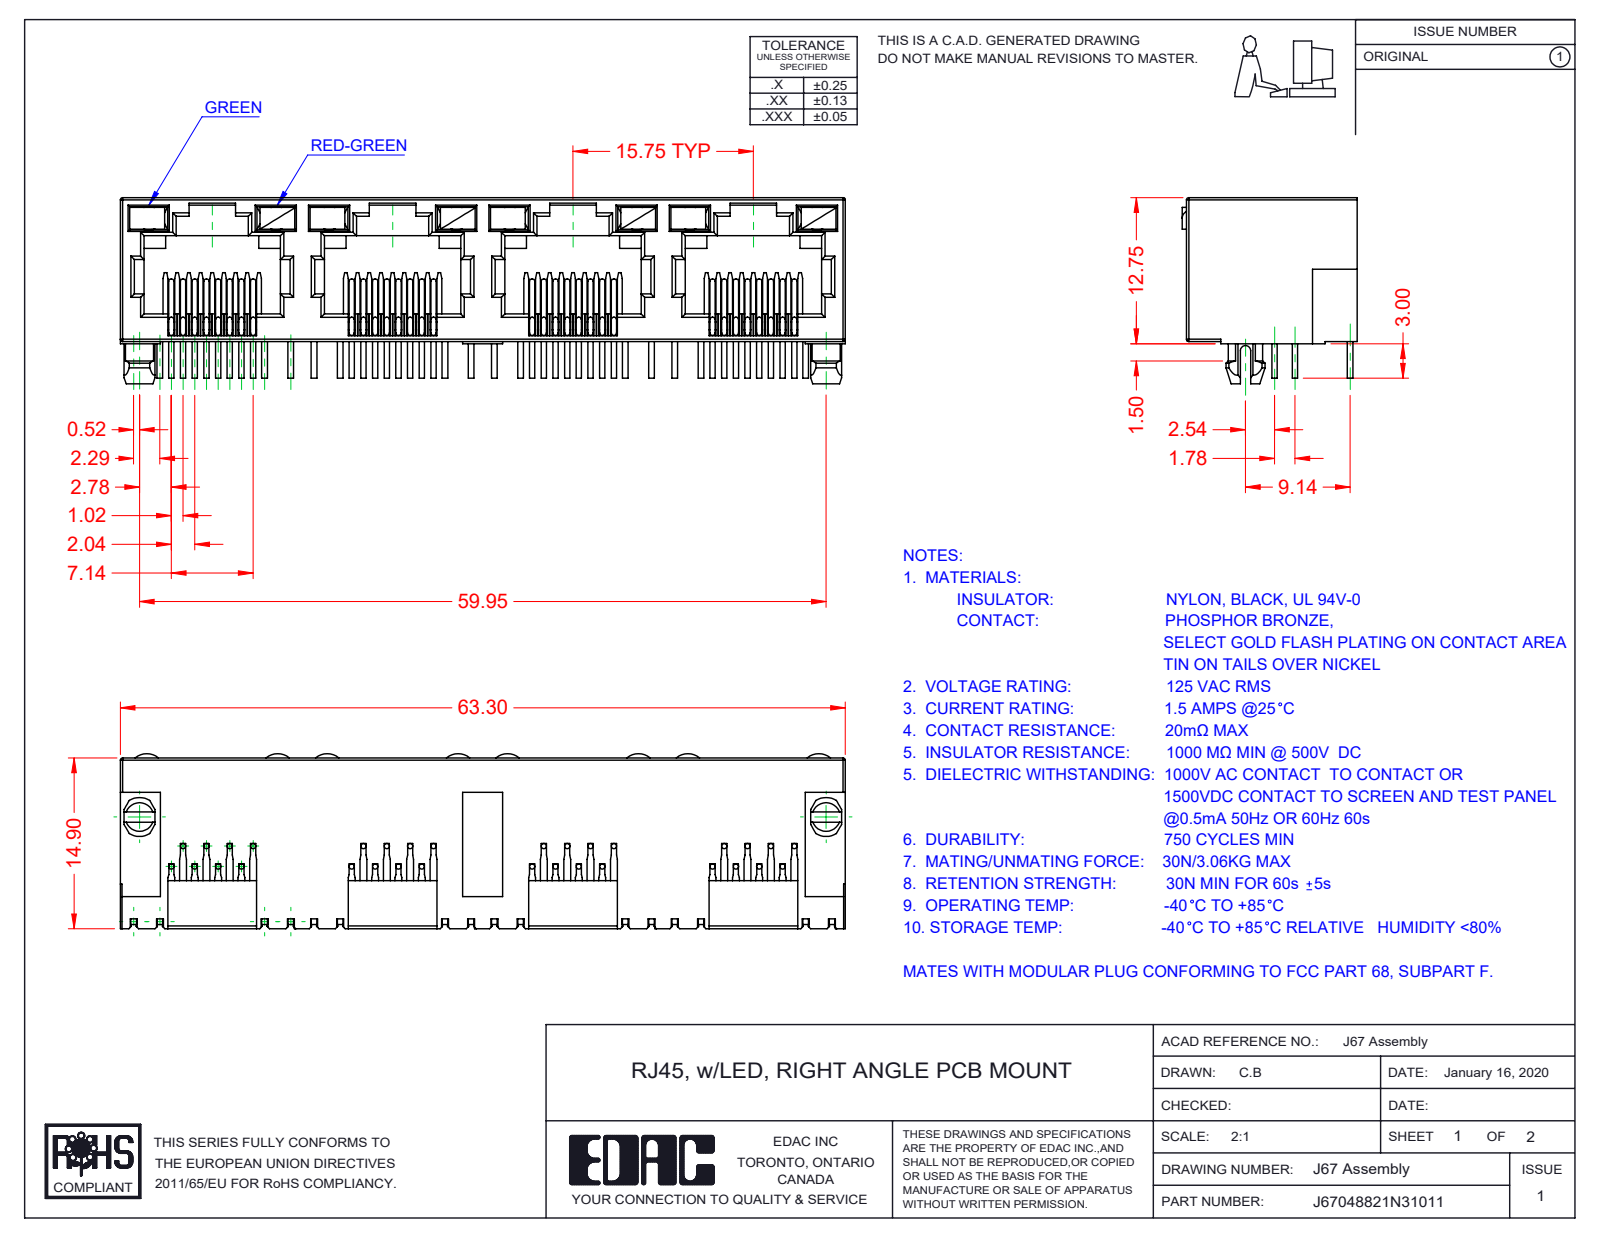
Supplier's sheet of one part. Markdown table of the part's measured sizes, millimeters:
| quantity | value |
| --- | --- |
| part name | 67 Contacts; 67 LED RH_6-Red-Green; J67048822N36011; 67 Insulator (+1 more) |
| STEP written by | SolidWorks 2016 (CONFIG_CONTROL_DESIGN) |
| units | millimeters |
| bodies | 41 solids, 2473 faces (1781 planar, 484 cylindrical, 208 other) |
| overall size | 63.3 × 16.25 × 15.28 |
| volume | 5 159 mm³ |
| surface area | 11 573 mm² |
| round bosses / shafts (diameter × count) | 0.46 × 96 |
| partial cylindrical surfaces (radius × count) | 0.2 × 66, 0.3 × 29, 0.45 × 9, 1.55 × 8, 1.5 × 2, 1.7 × 2, 0.35 × 1, 1 × 1 |
| main face-to-face distances | 0.5, 12.55, 1.89, 0.89, 10, 15.75, 1, 1.39, 11, 11.89 |
